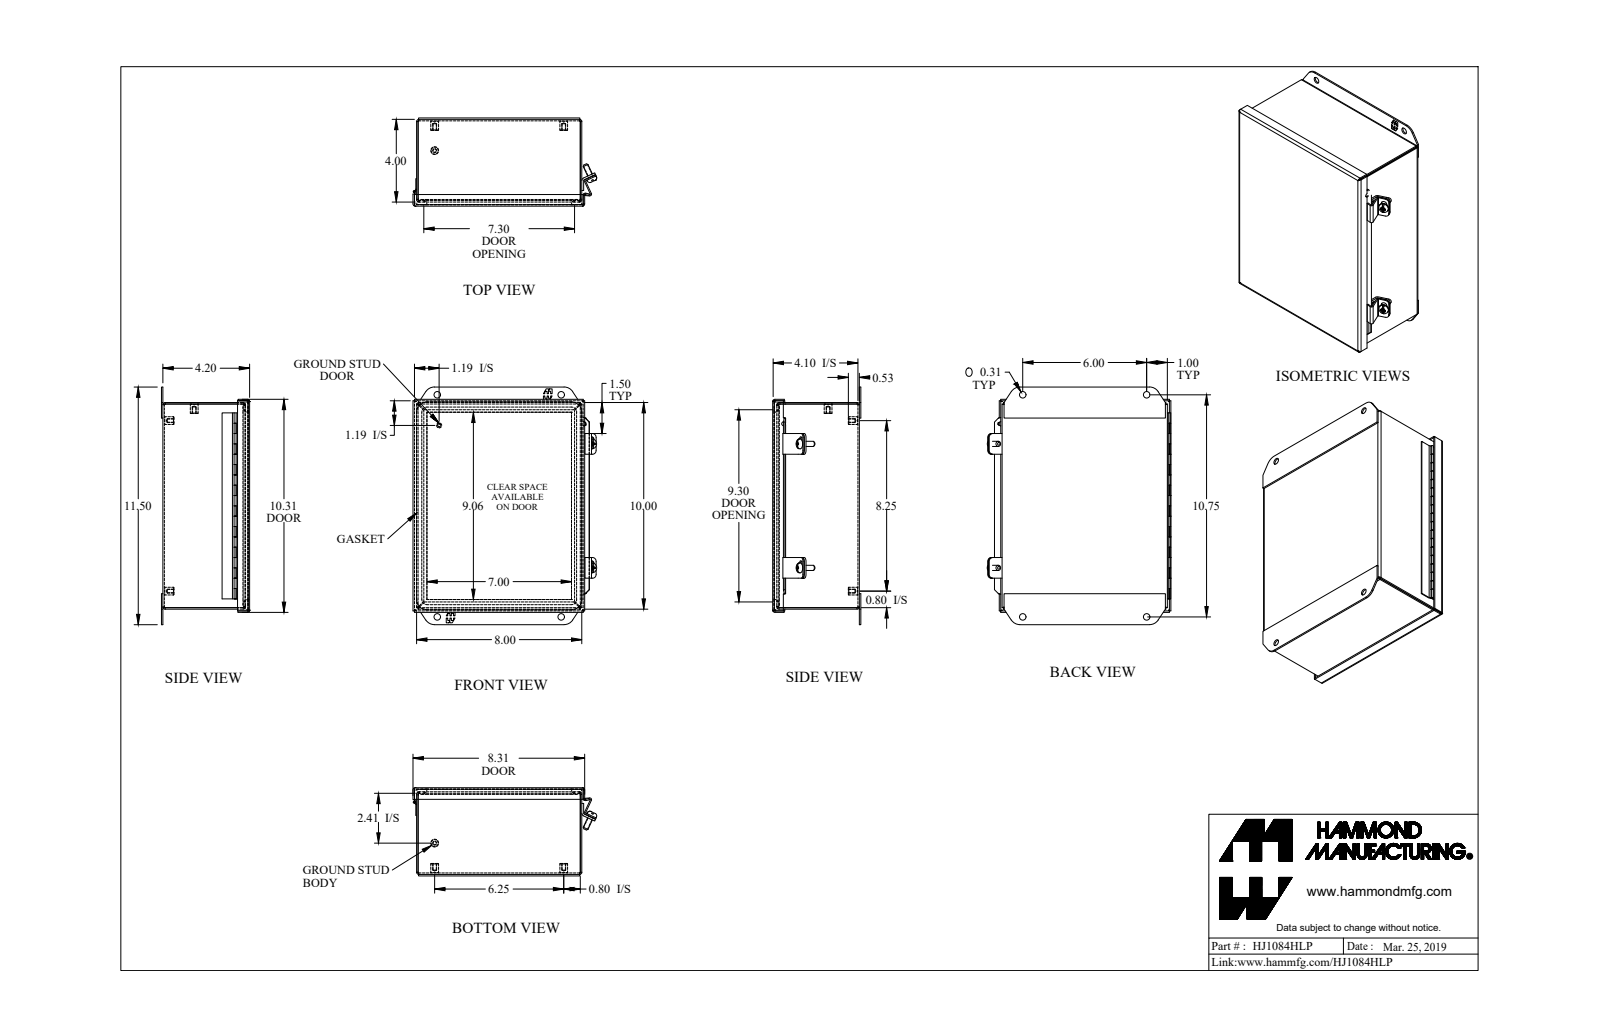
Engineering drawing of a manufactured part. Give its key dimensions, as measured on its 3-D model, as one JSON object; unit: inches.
{"part_name": "HJ1084HLP", "step_written_by": "SolidWorks 2018 (AUTOMOTIVE_DESIGN)", "units": "inches", "bodies": {"solids": 20, "faces": 745, "planar": 398, "cylindrical": 219, "other": 128}, "overall_size": [11.5, 8.896, 4.269], "volume_in3": 29.91, "surface_area_in2": 842.5, "round_holes": [[0.156, 5], [0.313, 4], [0.213, 2], [0.05, 1]], "round_bosses_or_shafts": [[0.375, 5], [0.25, 3], [0.48, 2], [0.188, 1], [0.1, 1], [0.045, 1]], "partial_cylinders_radius": [[0.25, 16], [0.036, 13], [0.108, 13], [0.01, 4], [0.141, 4], [0.188, 4], [0.499, 4], [0.5, 4]], "face_to_face_distances": [0.072, 4.125, 4.197, 4.053, 7.928, 9.928, 8, 7.856, 10, 9.856], "hole_center_spacings": [1.257, 9.501, 6, 6.252, 11.304, 8.25, 10.35, 10.75]}
